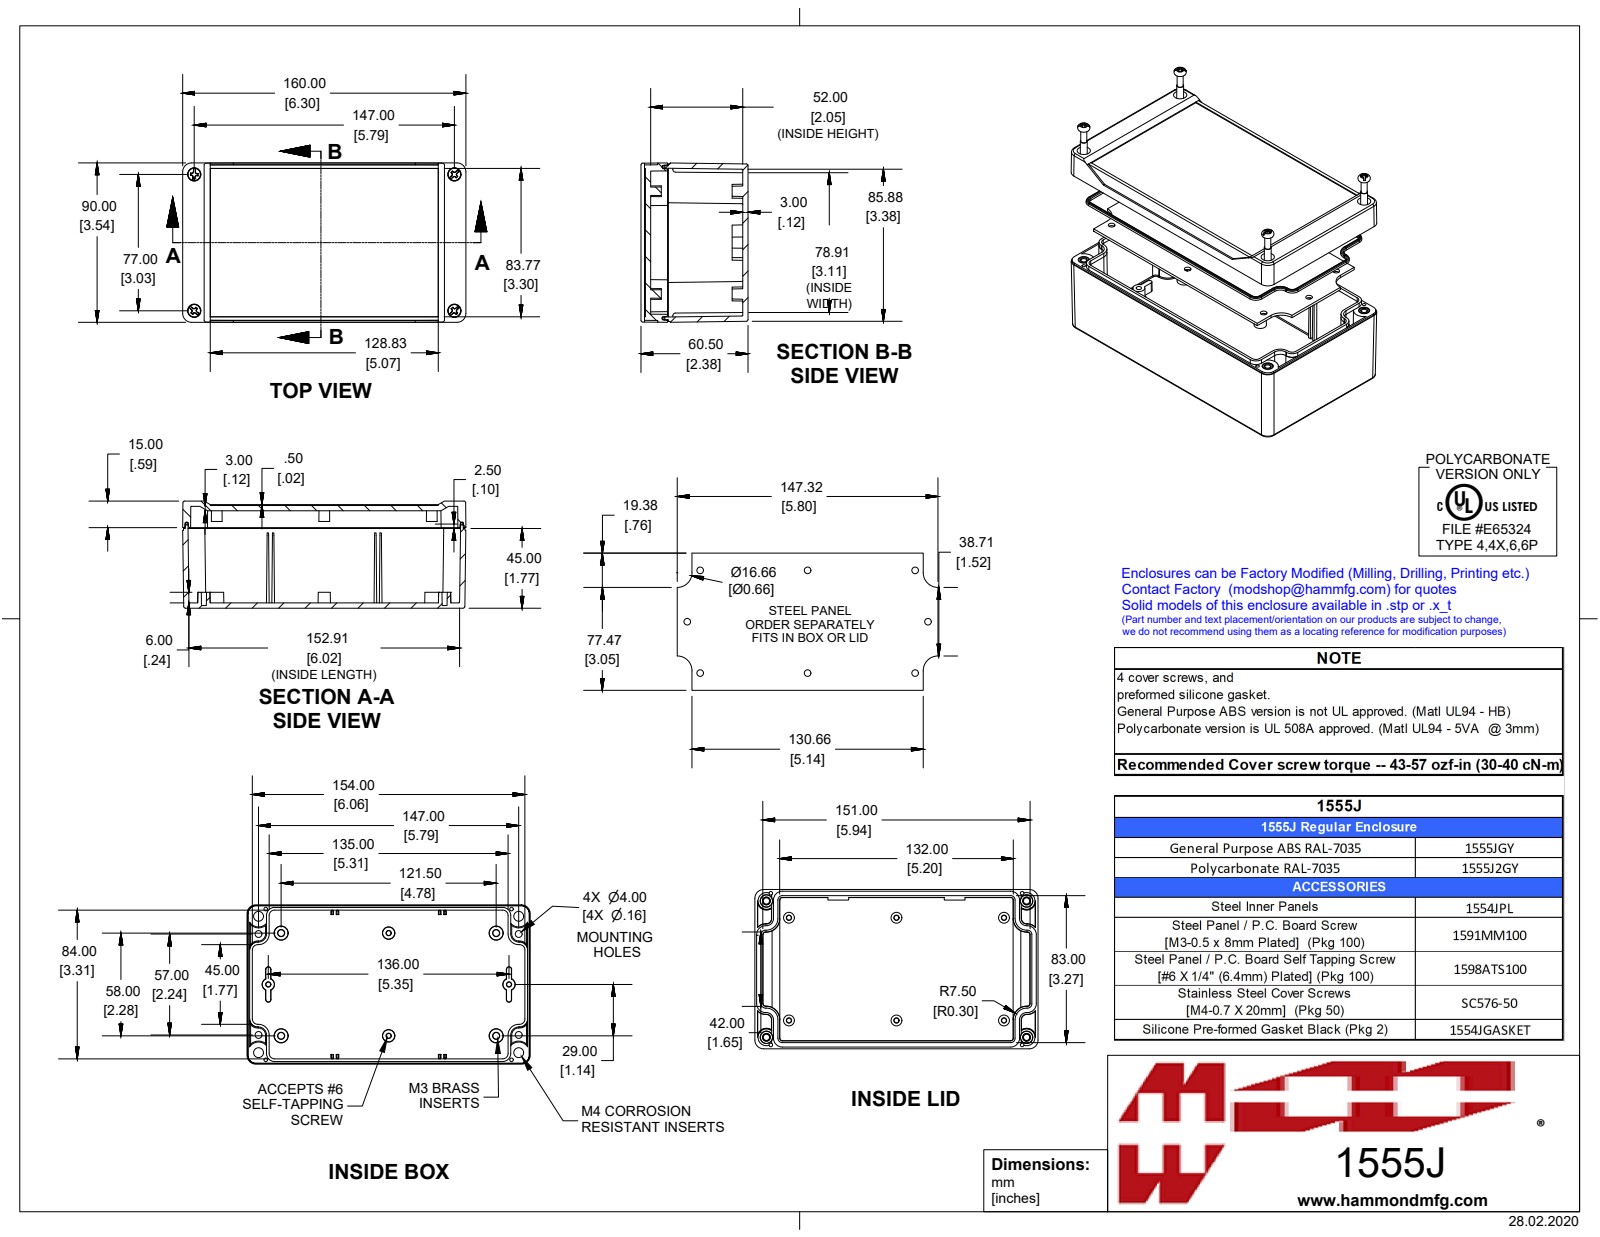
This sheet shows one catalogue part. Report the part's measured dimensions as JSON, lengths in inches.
{"part_name": "1555J2GY", "step_written_by": "SolidWorks 2019 (AUTOMOTIVE_DESIGN)", "units": "inches", "bodies": {"solids": 15, "faces": 1366, "planar": 408, "cylindrical": 348, "other": 610}, "overall_size": [6.299, 3.543, 2.382], "volume_in3": 11.35, "surface_area_in2": 214, "round_holes": [[0.079, 8], [0.097, 4], [0.128, 4], [0.138, 4], [0.276, 4]], "round_bosses_or_shafts": [[0.25, 4], [0.218, 4], [0.21, 4], [0.19, 4], [0.154, 4], [0.153, 4], [0.15, 4], [0.135, 4]], "partial_cylinders_radius": [[0.02, 24], [0.177, 12], [0.039, 8], [0.118, 8], [0.197, 8], [0.187, 4], [0.236, 4], [0.059, 3]], "face_to_face_distances": [0.118, 2.165, 2.283, 2.047, 0.059, 0.374, 0.492, 0.433, 0.138, 0.177], "hole_center_spacings": [0.197, 0.626, 0.678, 2.704, 2.857, 3.204, 5.215, 5.299]}
